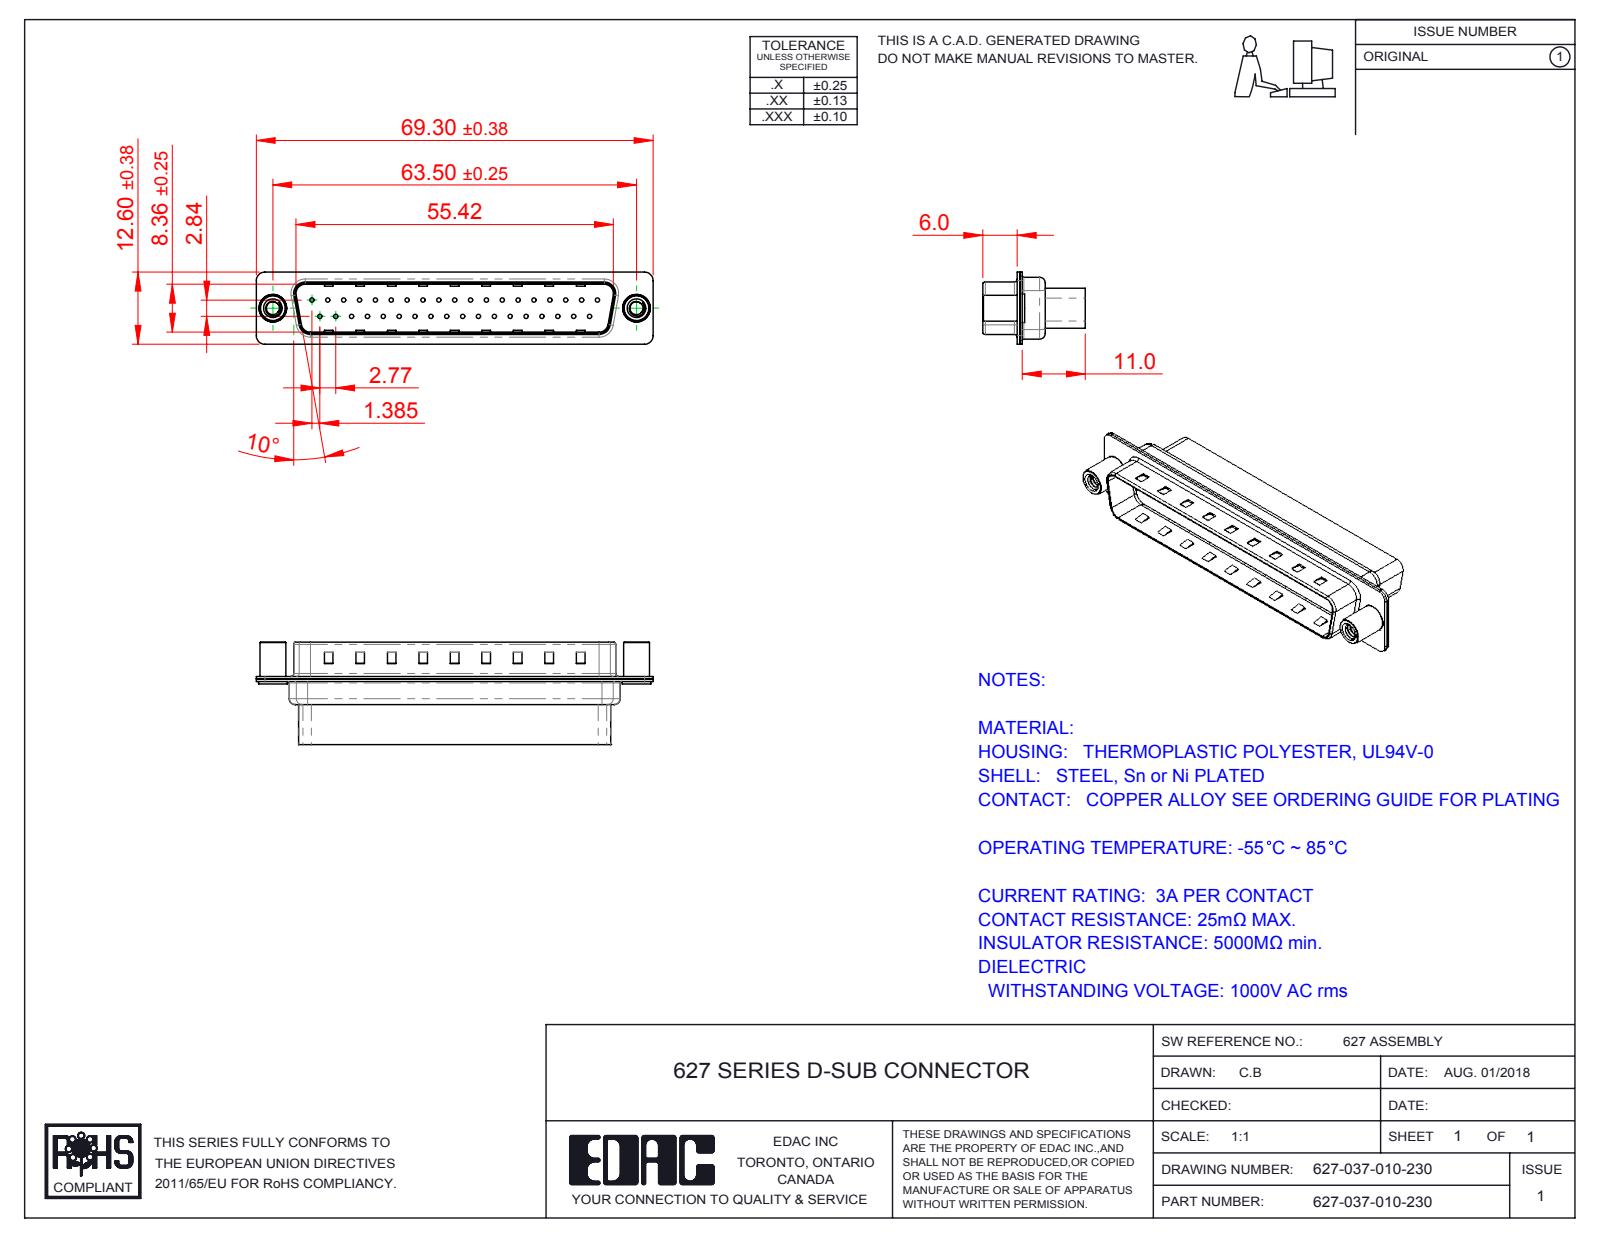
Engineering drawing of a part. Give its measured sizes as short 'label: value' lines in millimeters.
name: 627 Shell Front_37 Contacts; 627 Housing_37 HP; 627-037-010-230; 627 4-40 Threaded Standoff (+1 more)
written by: SolidWorks 2016 (CONFIG_CONTROL_DESIGN)
unit: mm
bodies: 5 solids, 742 faces (279 planar, 391 cylindrical, 72 other)
size: 69.3 × 17.9 × 12.6
volume: 5 087 mm³; area: 9 232 mm²
holes: 37× ⌀0.75, 37× ⌀1.6, 37× ⌀2, 2× ⌀2.26, 2× ⌀4, 2× ⌀4.8
bosses: 2× ⌀5, 2× ⌀4.9, 2× ⌀4.5
rounds: 16× R1.5, 12× R2, 8× R0.5, 8× R1.6, 4× R0.25, 4× R0.6, 4× R0.65, 4× R0.9
face distances: 0.4, 0.82, 9.58, 0.68, 7.68, 0.45, 1.08, 8.08, 8.76, 7
hole spacings: 3.16, 2.77, 5.54, 8.31, 5.04, 10.1, 11.08, 12.78
